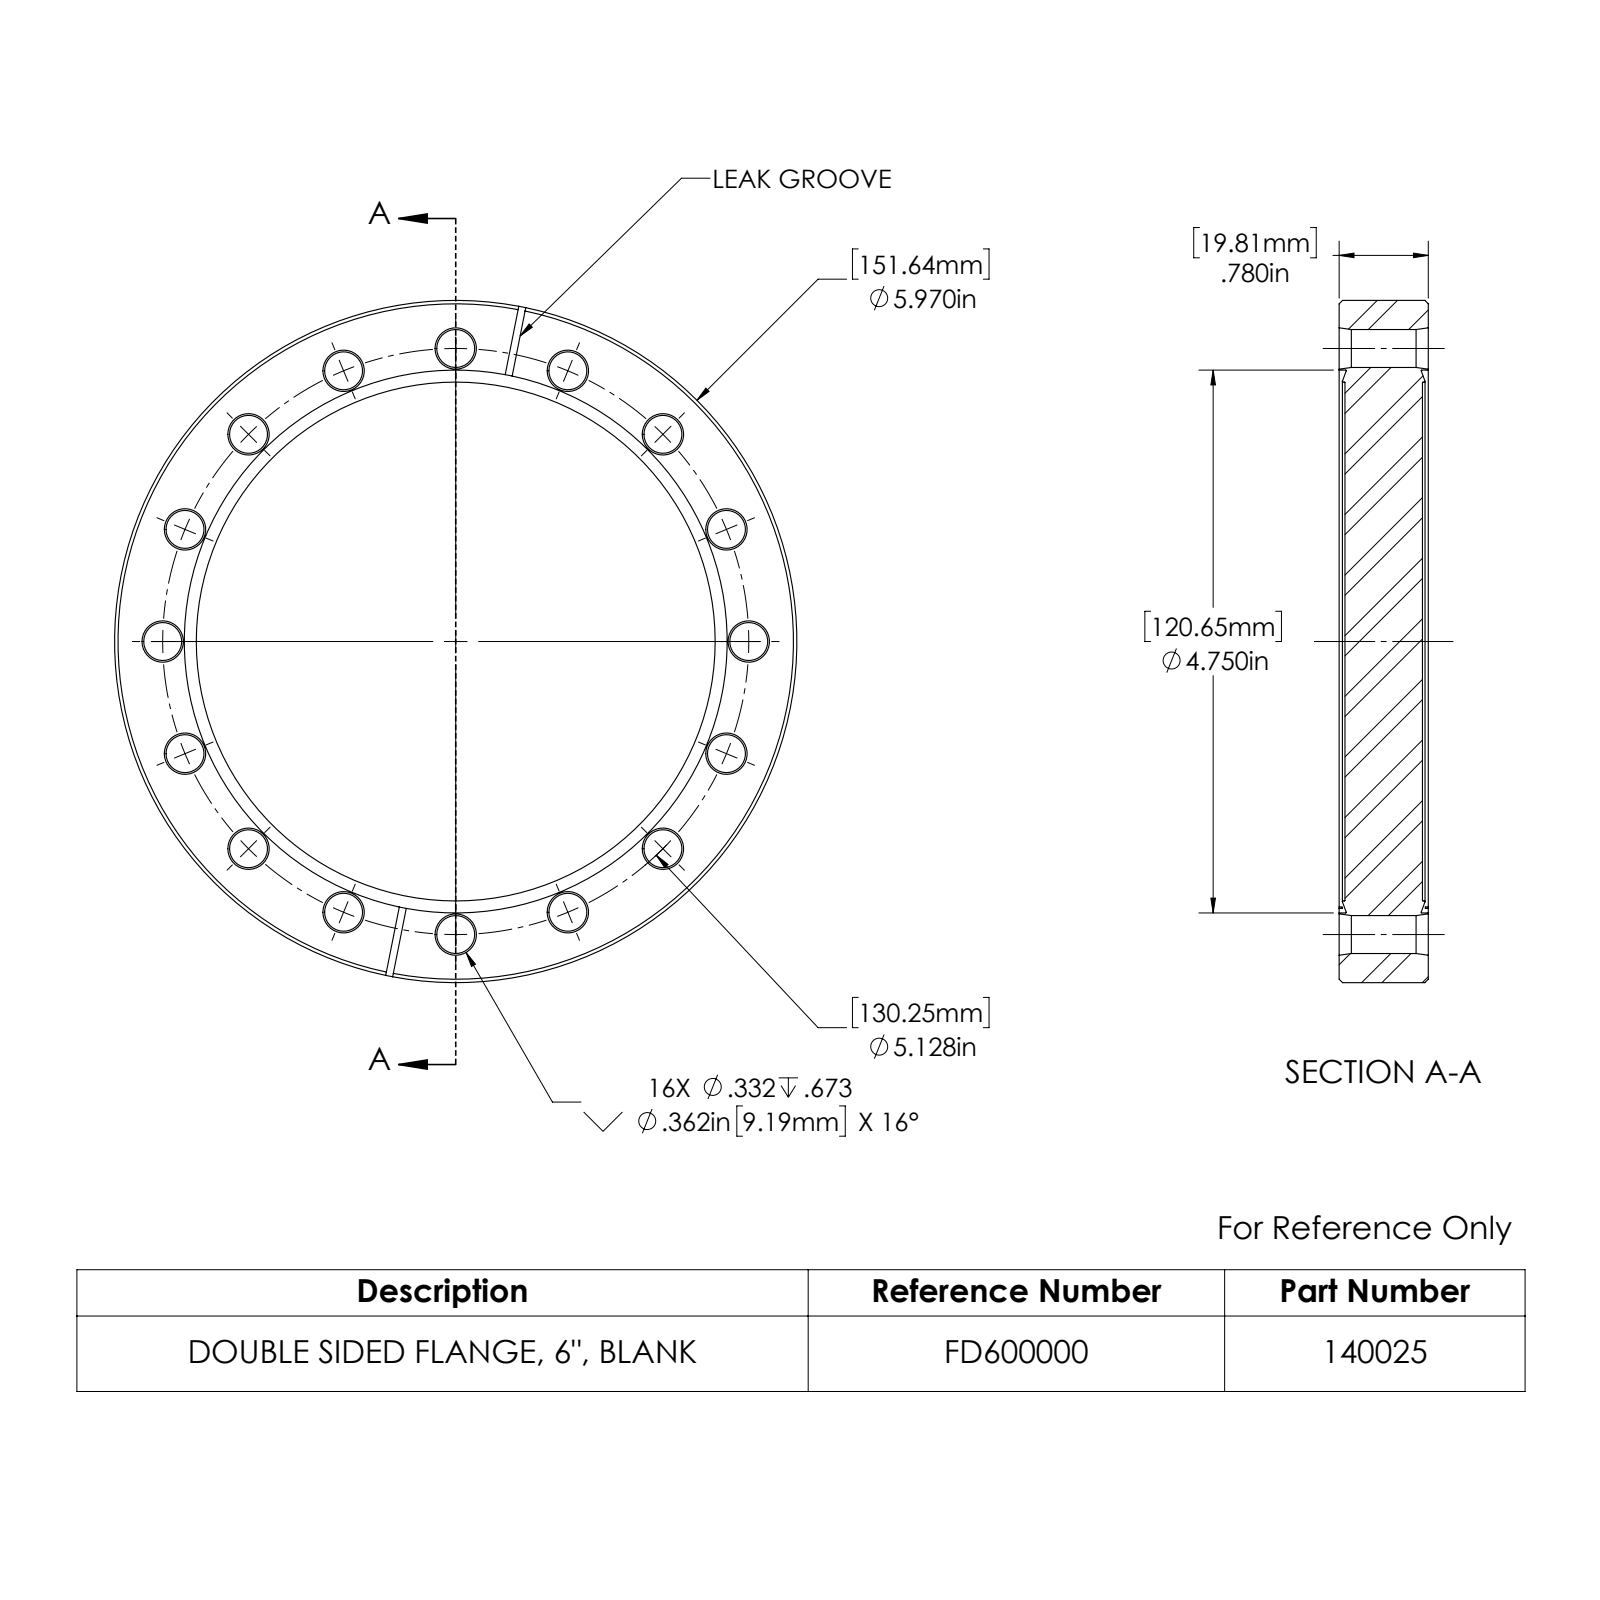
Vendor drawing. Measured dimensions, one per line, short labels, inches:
name: 140025_B
written by: SolidWorks 2022 (CONFIG_CONTROL_DESIGN)
unit: in
bodies: 1 solid, 146 faces (14 planar, 46 cylindrical, 86 other)
size: 5.97 × 5.97 × 0.78
volume: 18.9 in³; area: 82.86 in²
holes: 16× ⌀0.332, 1× ⌀4.54, 1× ⌀4.75
bosses: 1× ⌀5.97
rounds: 4× R1.25
face distances: 0.678, 0.729, 0.051, 0.051, 0.729, 0.78, 0.062, 0.061, 0.063
hole spacings: 1, 4.264, 4.738, 5.03, 1.963, 2.564, 3.626, 2.849
